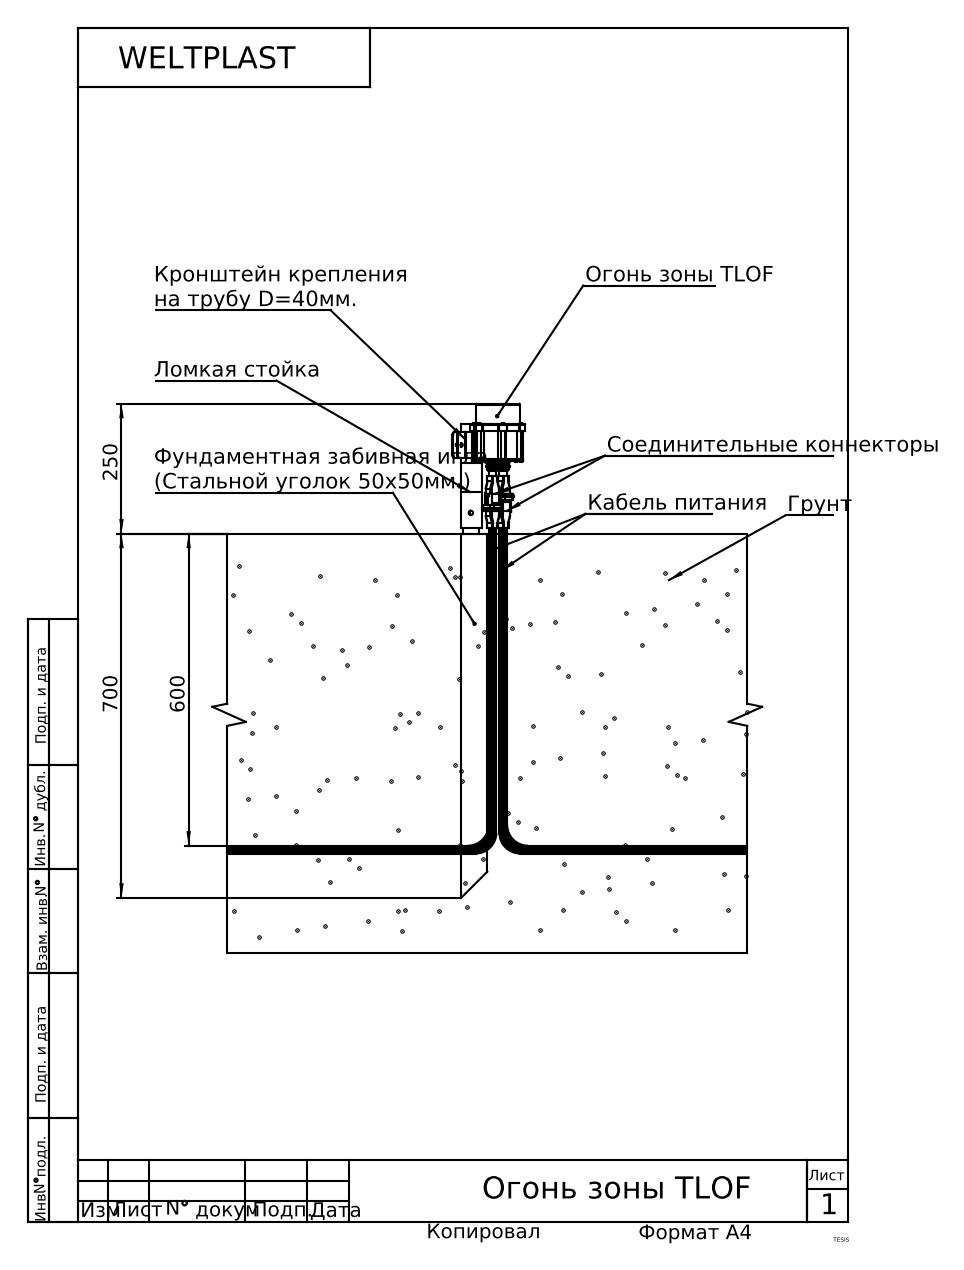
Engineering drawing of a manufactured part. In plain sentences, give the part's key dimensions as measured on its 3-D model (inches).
The part is named "конектор зажим; Скоба_крепления ИГЛА; Конектор мама Сборка 1; LLC-AB-60 (+8 more)". Its 3-D file was written by "SolidWorks 2017 (AUTOMOTIVE_DESIGN)". It is 44 solids with 3008 faces: 885 planar, 1069 cylindrical and 1054 other. Overall it measures 37.402 by 5.663 by 5.512 inches. Its volume is 43.83 cubic inches and its surface area 655.8 square inches. Round holes: 8 of diameter 0.209, 6 of diameter 0.142, 6 of diameter 0.173, 6 of diameter 0.177, 6 of diameter 0.248, 3 of diameter 0.098, 3 of diameter 0.103, 2 of diameter 0.165, 2 of diameter 0.236, 2 of diameter 0.496, 2 of diameter 0.797, 1 of diameter 0.327. Round bosses or shafts: 8 of diameter 0.299, 8 of diameter 0.157, 2 of diameter 0.846, 2 of diameter 0.776, 2 of diameter 0.591, 2 of diameter 0.413, 2 of diameter 0.236, 1 of diameter 3.346. Partial cylindrical surfaces (rounded edges, fillets, slot ends): 45 of radius 0.197, 36 of radius 0.079, 19 of radius 0.039, 18 of radius 0.177, 14 of radius 0.059, 12 of radius 0.118, 8 of radius 0.02, 8 of radius 0.098. The main face-to-face distances are 0.157, 0.079, 0.059, 0.118, 0.374, 0.039, 0.217, 2.52, 2.362, 1.575. The hole center spacings are 1.87, 3.239, 1.914, 0.114, 1.102, 2.198, 1.103, 2.197.
